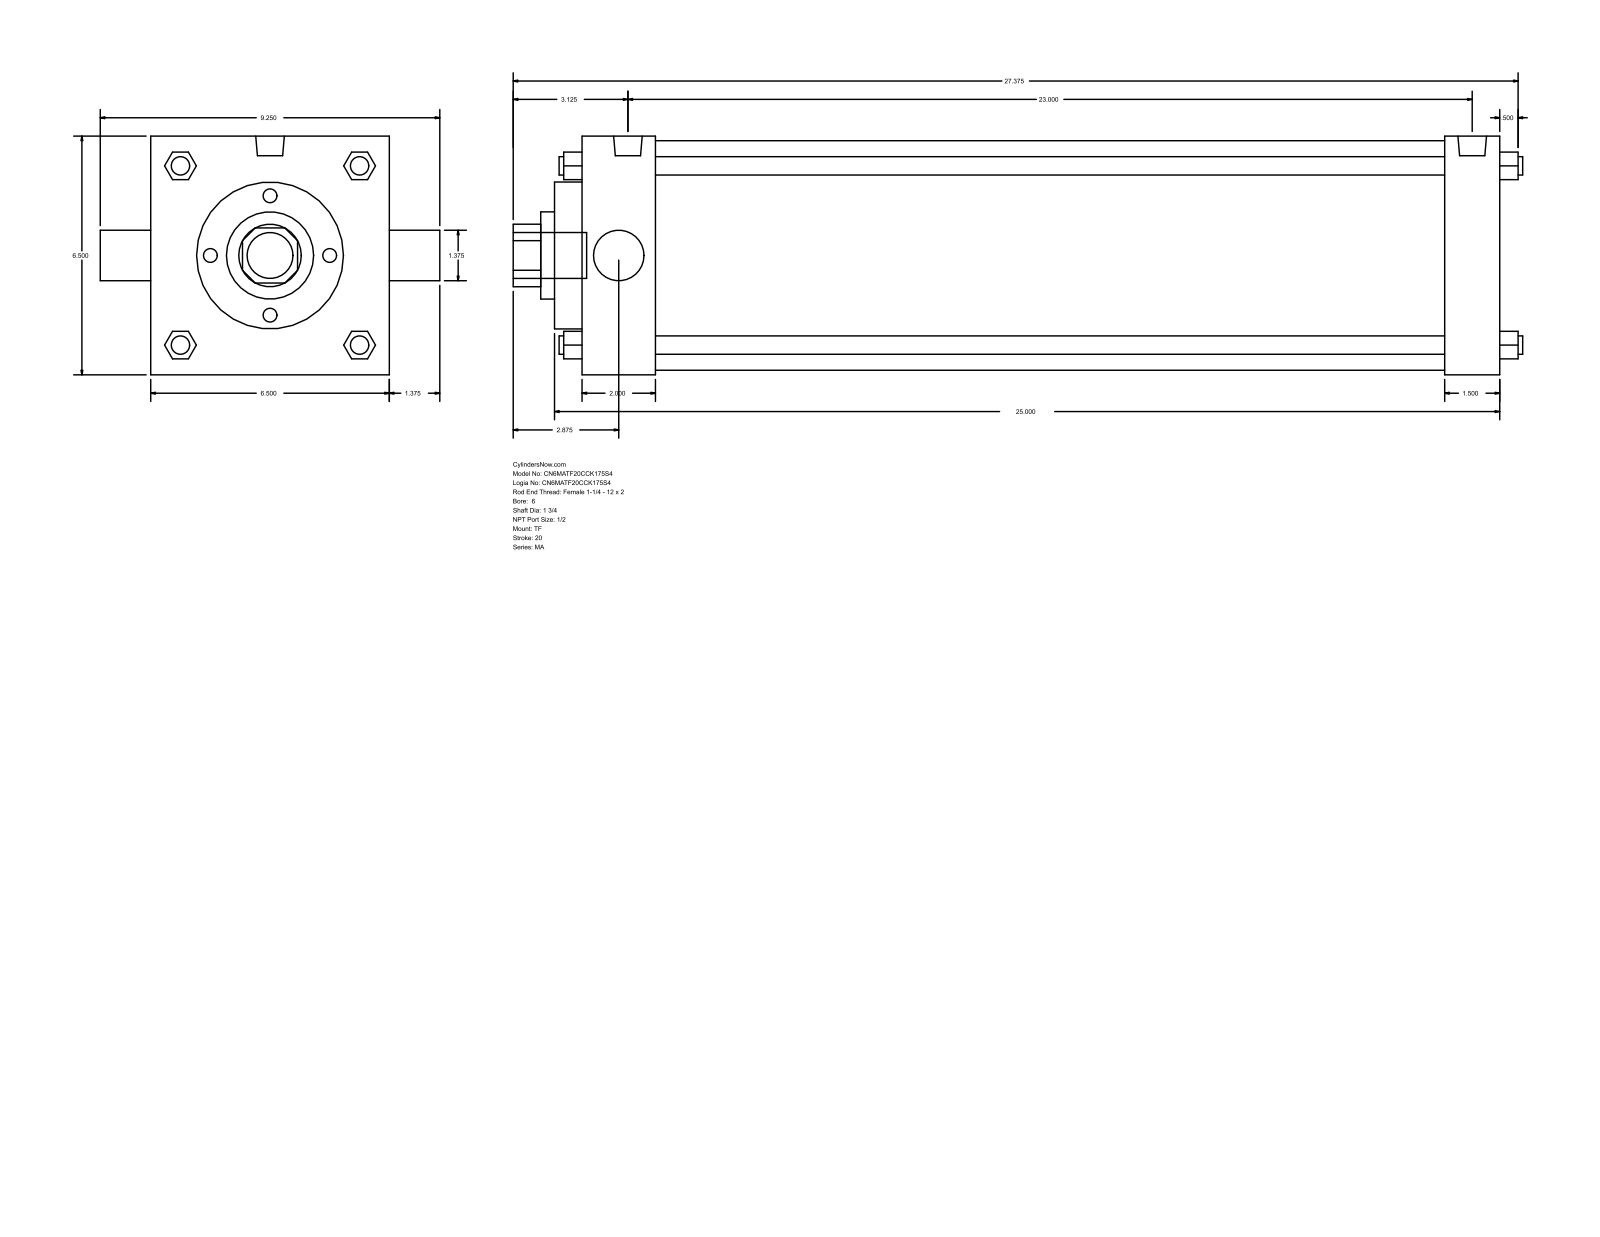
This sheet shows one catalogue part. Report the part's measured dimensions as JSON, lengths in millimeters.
{"part_name": "MA_TF__0600_1.75", "step_written_by": "GSSL Pune (CONFIG_CONTROL_DESIGN)", "units": "millimeters", "bodies": {"solids": 0, "faces": 122, "planar": 93, "cylindrical": 29, "other": 0}, "overall_size": [698.5, 234.95, 165.1], "round_holes": [[34.92, 1], [44.45, 1], [60.33, 1], [101.6, 1], [158.75, 1]], "round_bosses_or_shafts": [[12.7, 4], [17.46, 3], [19.77, 2], [31.75, 1]], "partial_cylinders_radius": [[21.63, 1]], "face_to_face_distances": [165.1, 635, 19.05, 38.1, 50.8, 584.2, 596.9, 546.1, 69.85, 615.95]}
